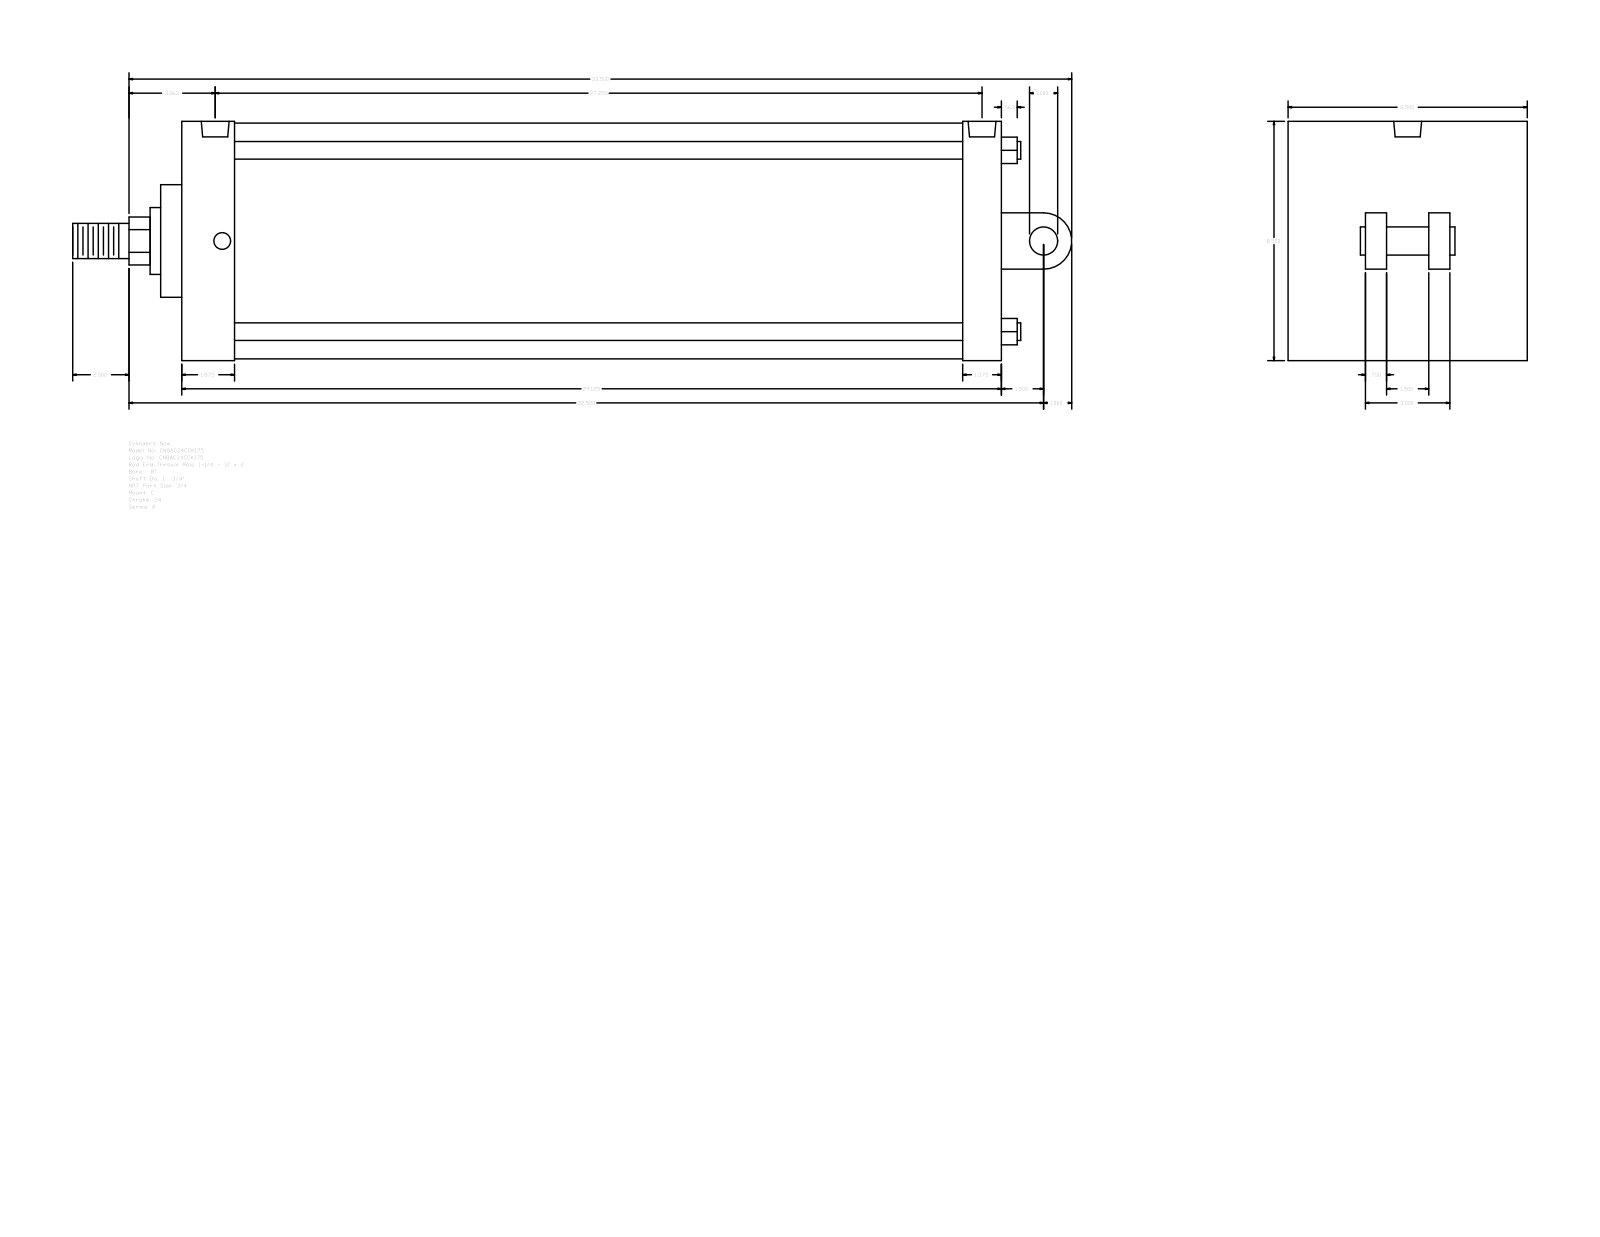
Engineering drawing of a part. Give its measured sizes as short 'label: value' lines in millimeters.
name: A_C__0800_1.75
written by: GSSL Pune (CONFIG_CONTROL_DESIGN)
unit: mm
bodies: 0 solids, 104 faces (75 planar, 29 cylindrical, 0 other)
size: 901.7 × 215.9 × 215.9
holes: 4× ⌀15.08, 2× ⌀25.12
bosses: 4× ⌀15.88, 1× ⌀212.72, 1× ⌀60.33, 1× ⌀44.45, 1× ⌀31.75, 1× ⌀25.4
rounds: 1× R21.63, 1× R25.4
face distances: 739.78, 215.9, 19.05, 57.15, 47.63, 692.15, 704.86, 657.23, 34.92, 69.85
hole spacings: 6.35, 679.45, 685.8, 692.15
